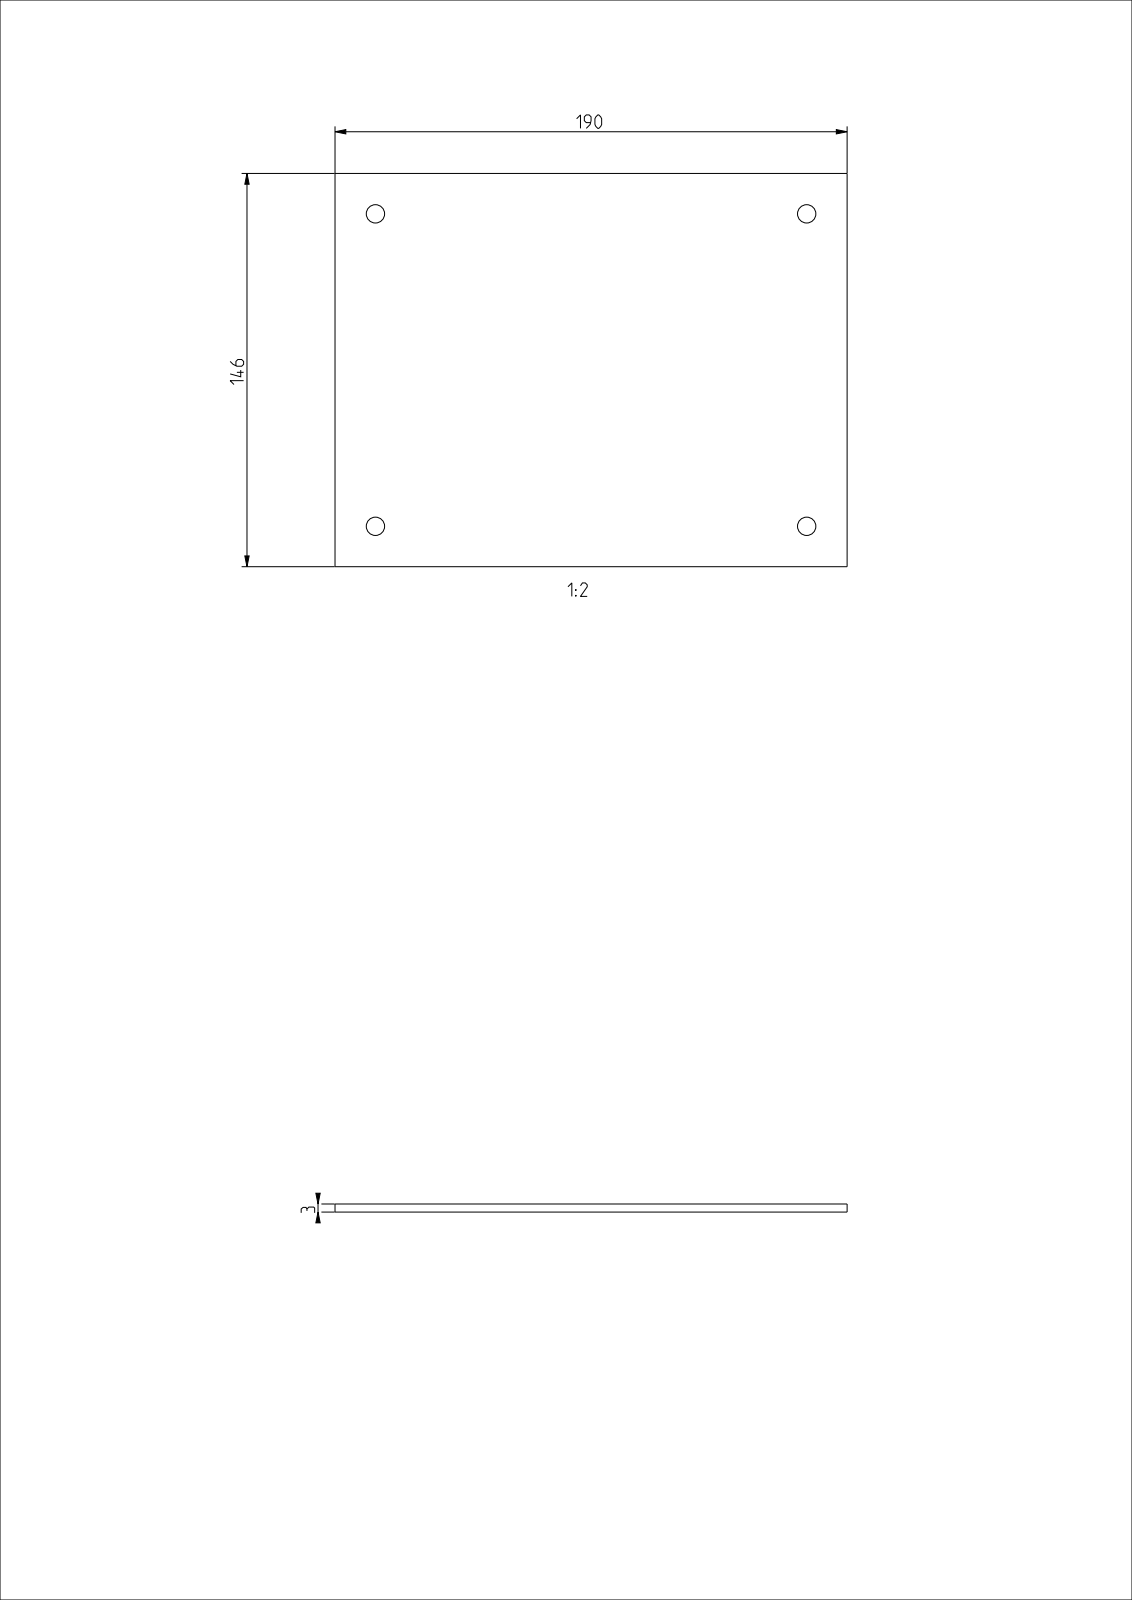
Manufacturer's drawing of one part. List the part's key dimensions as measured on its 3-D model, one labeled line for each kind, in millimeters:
Part name (STEP PRODUCT): T-00574; T-00915_ASM
STEP written by: CREO PARAMETRIC BY PTC INC, 2022024 (AUTOMOTIVE_DESIGN)
Units: millimetres
Bodies: 1 solid, 14 faces (6 planar, 8 cylindrical, 0 other)
Overall size (bounding box): 190 × 146 × 3
Volume: 82 784 mm³ · Surface area: 57 462 mm²
Round holes (diameter × count): ⌀6.8 ×4
Main face-to-face distances: 3, 146, 190
Hole centre spacings: 116, 160, 197.63
